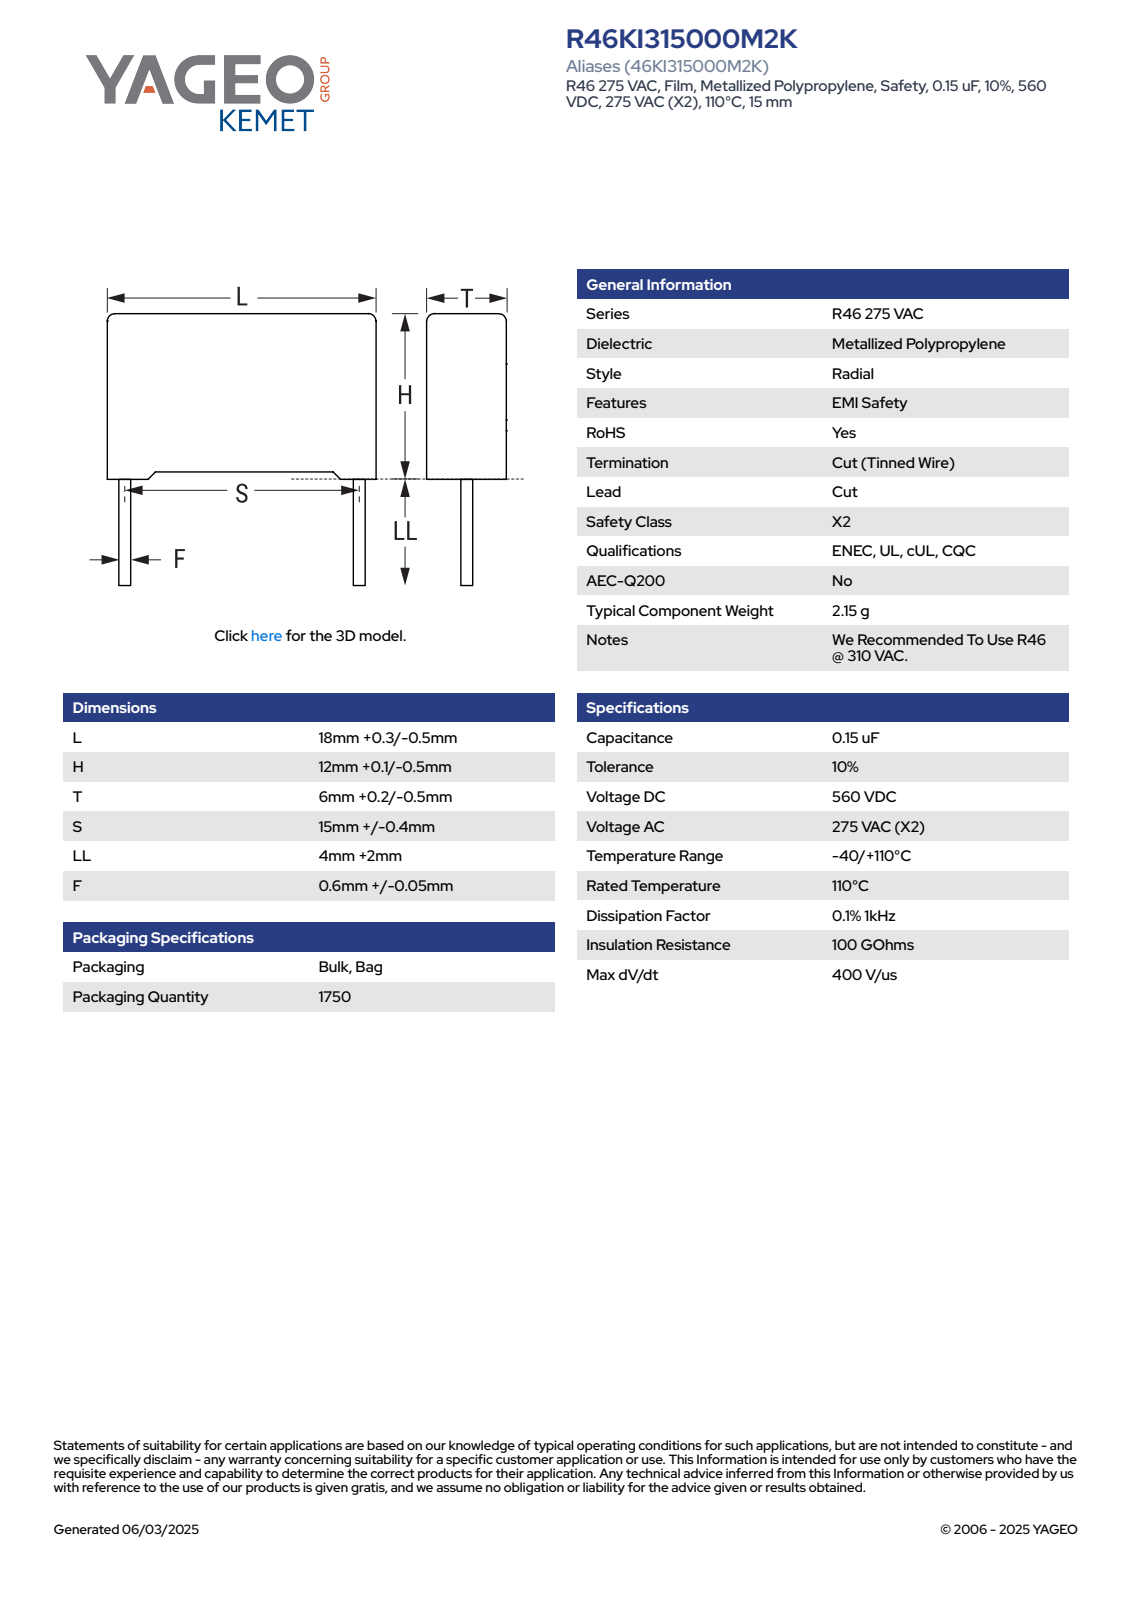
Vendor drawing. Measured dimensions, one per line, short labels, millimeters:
name: CFR_RB2_18X12X6_L18.3H12.1T6.2S15LL6F0.65
written by: SolidWorks 2021 (AUTOMOTIVE_DESIGN)
unit: mm
bodies: 4 solids, 85 faces (77 planar, 8 cylindrical, 0 other)
size: 18.3 × 18.1 × 6.21
volume: 1 305 mm³; area: 876 mm²
bosses: 2× ⌀0.65
rounds: 4× R0.5
face distances: 6.2, 11.35, 18.3, 0.61, 5.59, 0.75, 12.1, 0.42, 0.33, 11.68
